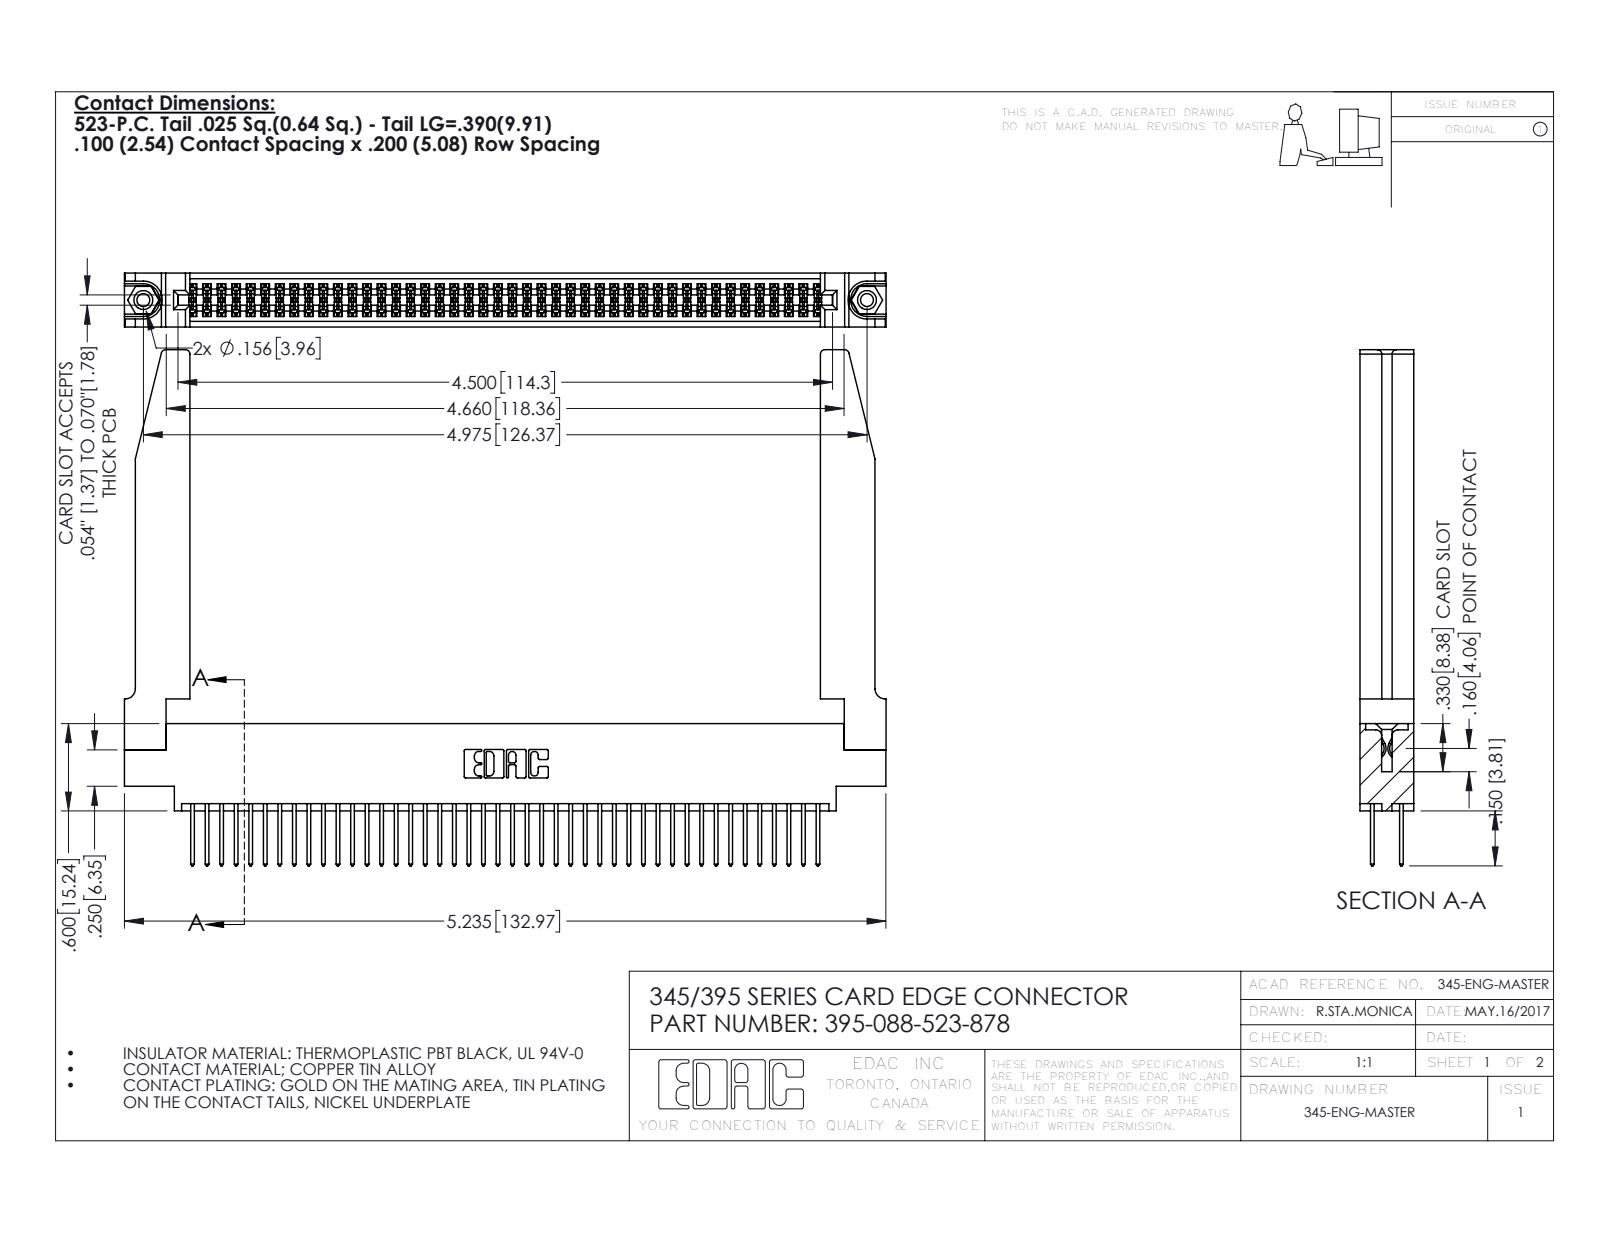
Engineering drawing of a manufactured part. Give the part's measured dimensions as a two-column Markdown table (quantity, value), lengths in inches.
| quantity | value |
| --- | --- |
| part name | 345 Part_0.170 Offset - 0.156 Dia-TH; 345-220-078_345-220-078; 345-250-001_345-250-001-102; 395-088-523-878 (+1 more) |
| STEP written by | SolidWorks 2016 (CONFIG_CONTROL_DESIGN) |
| units | inches |
| bodies | 93 solids, 4764 faces (3130 planar, 1582 cylindrical, 52 other) |
| overall size | 5.236 × 3.547 × 0.37 |
| volume | 1.268 in³ |
| surface area | 41.93 in² |
| round holes (diameter × count) | 0.089 × 2, 0.125 × 2, 0.156 × 2, 0.064 × 1 |
| round bosses / shafts (diameter × count) | 0.155 × 2 |
| partial cylindrical surfaces (radius × count) | 0.006 × 132, 0.01 × 88, 0.01 × 22, 0.03 × 8, 0.007 × 6, 0.031 × 6, 0.026 × 3, 0.014 × 2 |
| main face-to-face distances | 0.072, 0.298, 0.37, 0.2, 0.098, 0.272, 0.025, 0.225, 0.175, 0.148 |
| hole center spacings | 0.27, 4.739, 4.975 |
